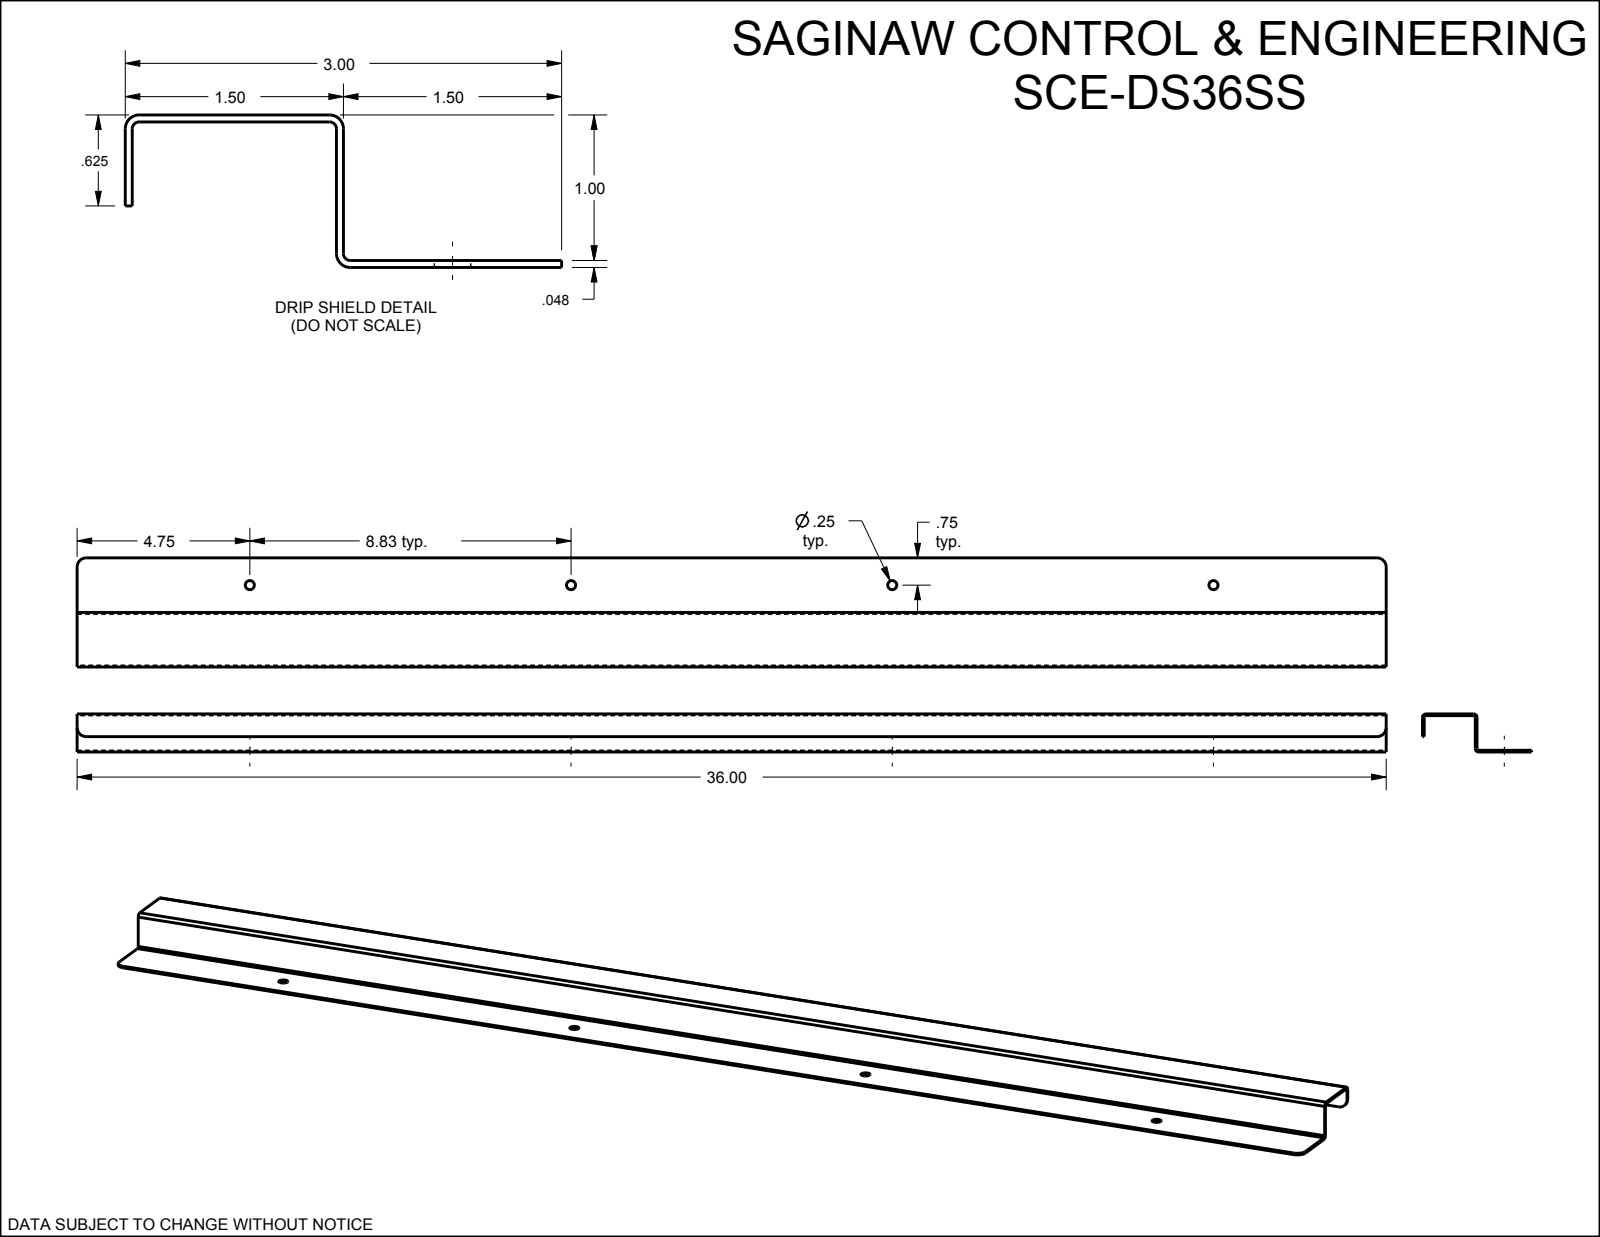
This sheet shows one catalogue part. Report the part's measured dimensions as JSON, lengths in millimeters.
{"part_name": "SCE-DS36SS6", "step_written_by": "SolidWorks 2019 (CONFIG_CONTROL_DESIGN)", "units": "millimeters", "bodies": {"solids": 1, "faces": 26, "planar": 12, "cylindrical": 14, "other": 0}, "overall_size": [914.4, 76.2, 26.6], "volume_mm3": 126800, "surface_area_mm2": 210600, "round_holes": [[6.4, 4]], "partial_cylinders_radius": [[6.4, 4], [1.2, 3], [2.4, 3]], "face_to_face_distances": [1.2, 25.4, 24.2, 26.6, 36.9, 38.1, 35.7, 10.7, 9.5, 14.7], "hole_center_spacings": [224.4, 448.7, 224.4, 673.1]}
